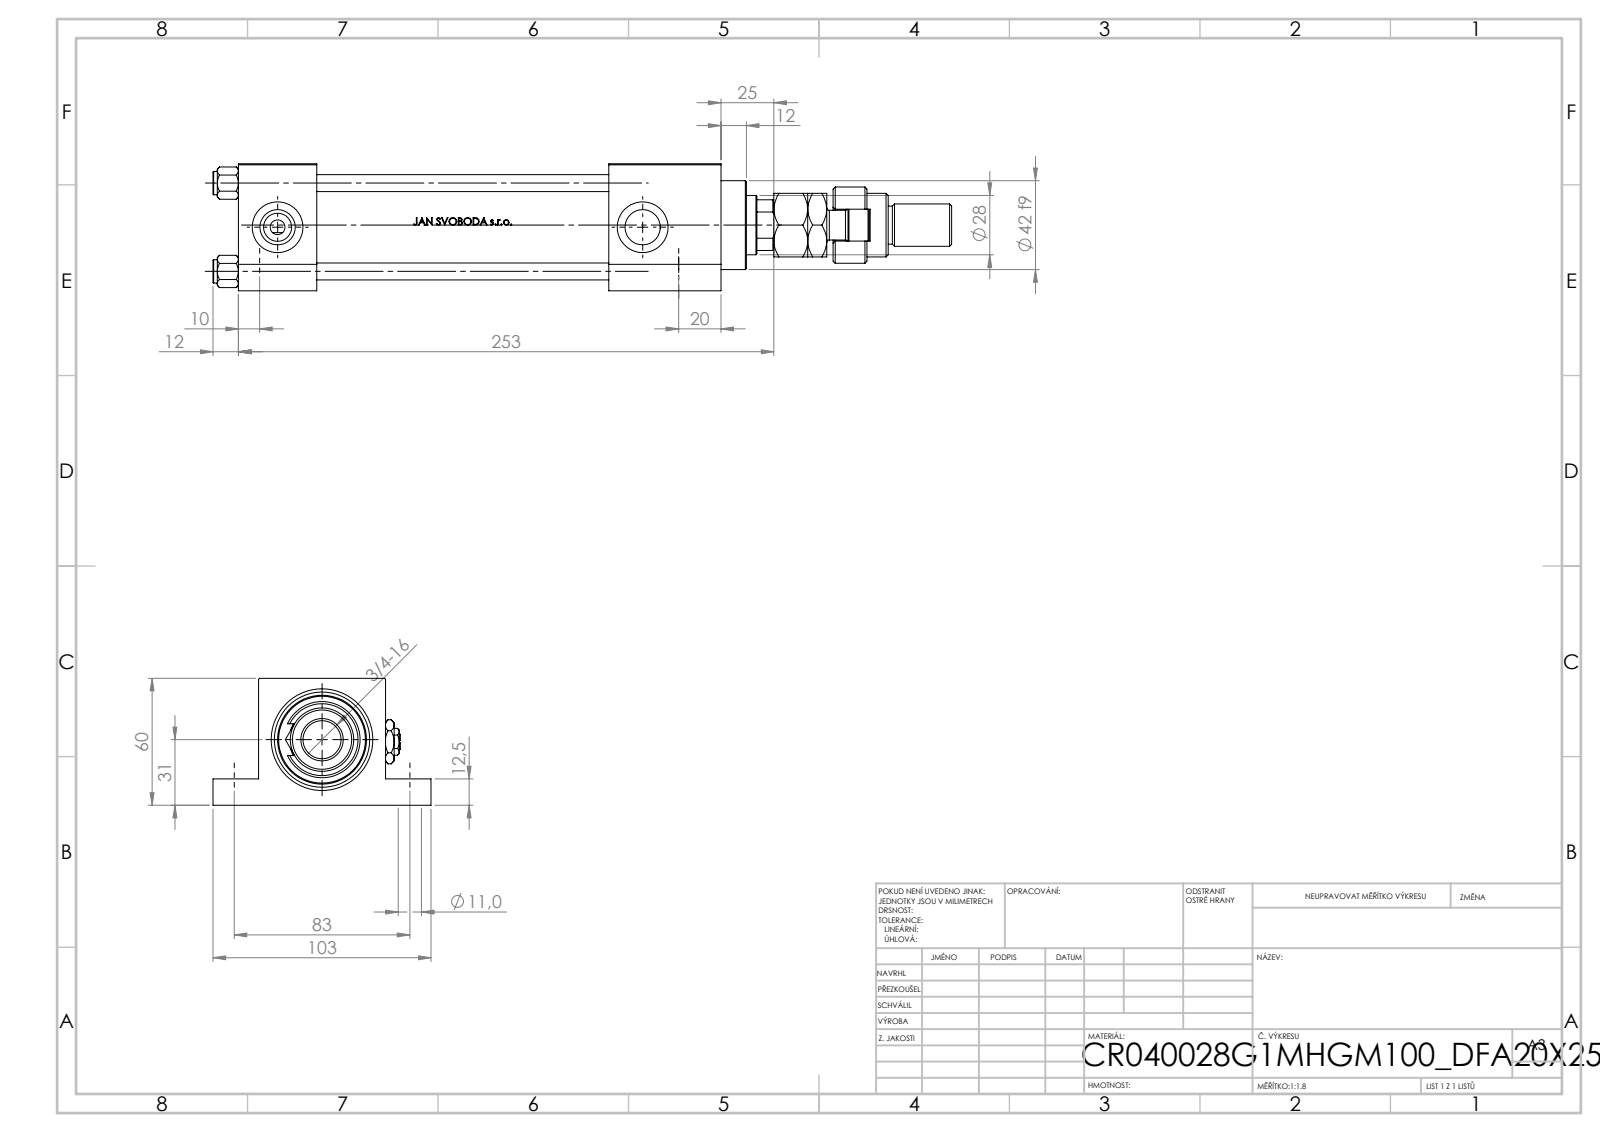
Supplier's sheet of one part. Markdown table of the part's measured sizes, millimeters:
| quantity | value |
| --- | --- |
| part name | V215CR_G_TYCINKA; NUT_M5_G; Zatka_pro_OIL_PORT; V215_VC_A (+4 more) |
| STEP written by | SolidWorks 2019 (CONFIG_CONTROL_DESIGN) |
| units | millimeters |
| bodies | 14 solids, 1220 faces (483 planar, 141 cylindrical, 596 other) |
| overall size | 349 × 103 × 60 |
| volume | 616 557 mm³ |
| surface area | 171 463 mm² |
| round holes (diameter × count) | 8 × 4, 11 × 4, 7 × 2, 16.66 × 2, 24 × 2, 18.5 × 1, 28 × 1, 31 × 1, 40 × 1, 45 × 1 |
| round bosses / shafts (diameter × count) | 11 × 4, 46 × 1, 42 × 1, 36 × 1, 30 × 1, 22 × 1, 20 × 1, 18 × 1 |
| partial cylindrical surfaces (radius × count) | 7.5 × 1, 12 × 1, 13.5 × 1 |
| main face-to-face distances | 60, 37, 12.5, 47.5, 53, 175, 138, 228, 191, 21.5 |
| hole center spacings | 41.7, 28.79, 30.2, 58.97, 83, 198, 214.69, 172.5 |
